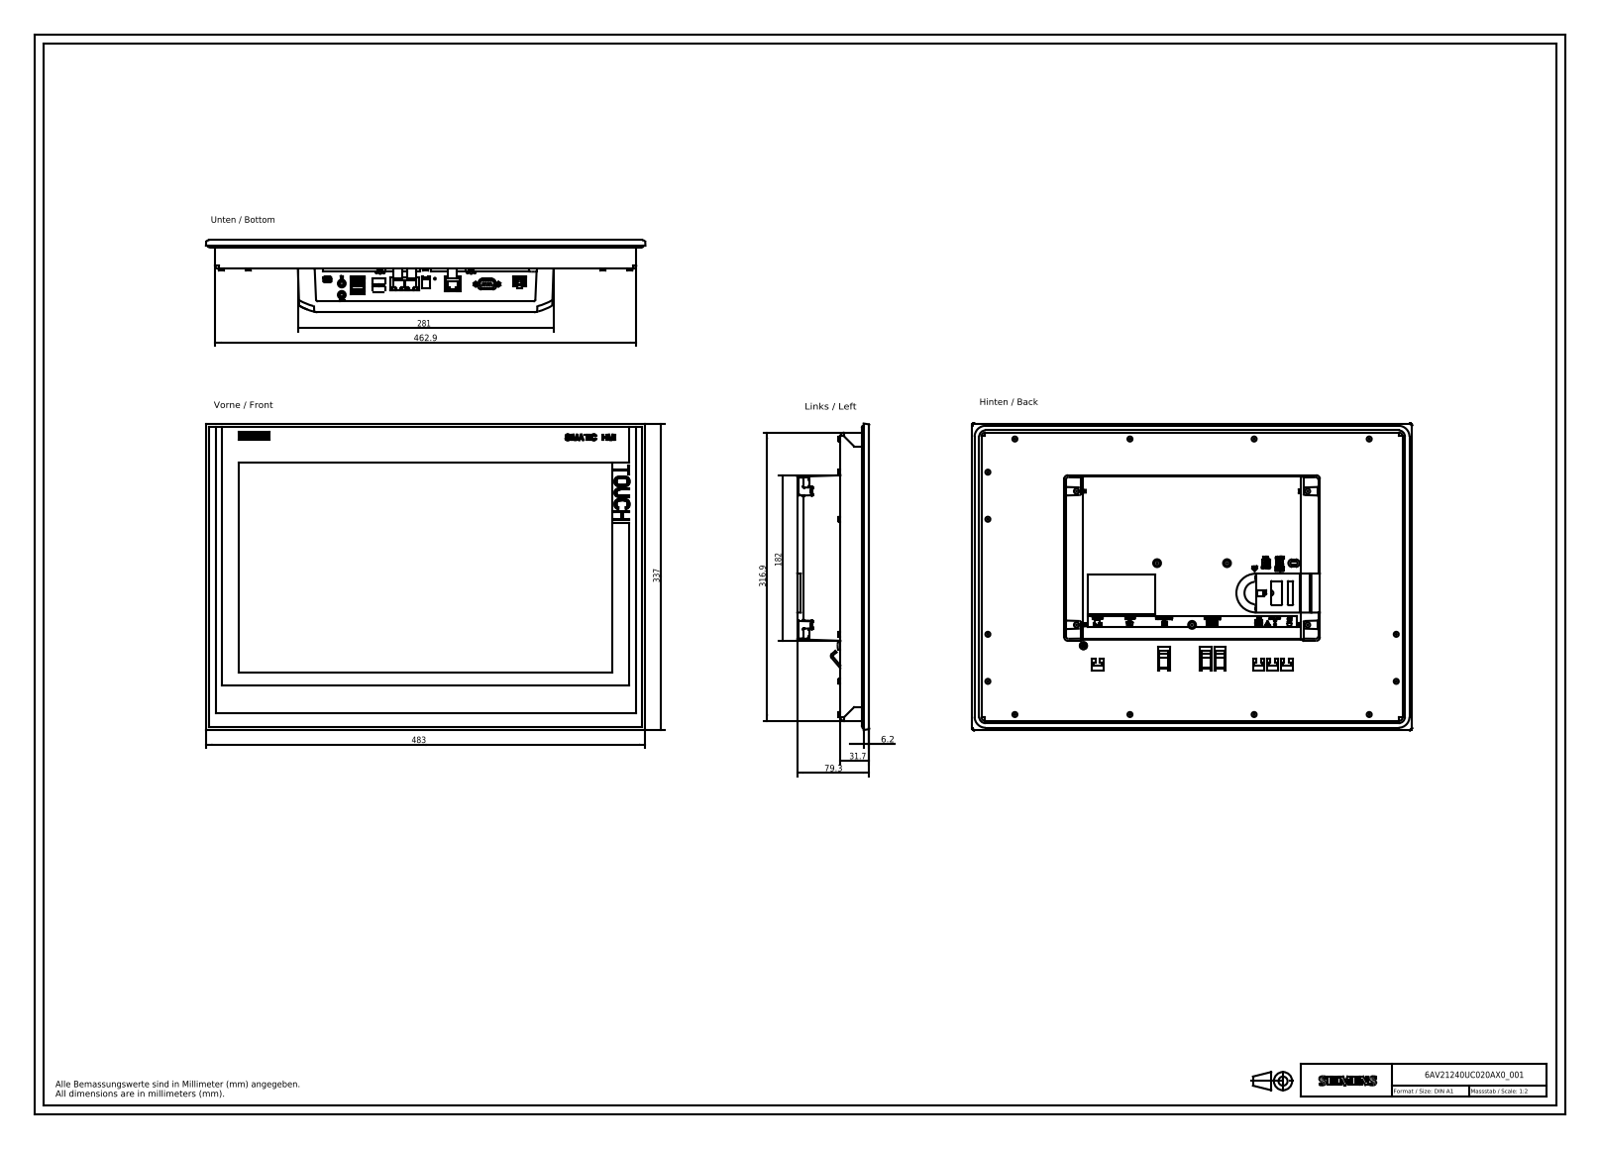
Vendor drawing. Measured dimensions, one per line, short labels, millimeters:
name: A5E30321192A_001; A5E30981575A_001; A5E30981571A_001; A5E30981561A_001 (+1 more)
written by: SIEMENS PLM Software NX 7.5 (AUTOMOTIVE_DESIGN)
unit: mm
bodies: 246 solids, 2762 faces (2294 planar, 220 cylindrical, 248 other)
size: 483 × 337 × 79.4
volume: 7 008 000 mm³; area: 580 098 mm²
holes: 9× ⌀0.8, 3× ⌀8.02, 2× ⌀1.81, 2× ⌀2.4, 2× ⌀2.84, 2× ⌀3.8, 2× ⌀8.5
bosses: 8× ⌀6, 2× ⌀7, 2× ⌀3.04, 2× ⌀3, 2× ⌀2.01, 1× ⌀8
rounds: 48× R0.84, 8× R1.26, 4× R0.98, 4× R1.85, 4× R3.95, 4× R6.98, 4× R12, 4× R12.02
face distances: 31, 9.5, 40.5, 8.5, 1, 39.5, 38.1, 39.1, 47.6, 78.6
hole spacings: 2.89, 2.74, 4.83, 5.48, 7.31, 8.22, 9.92, 12.5
